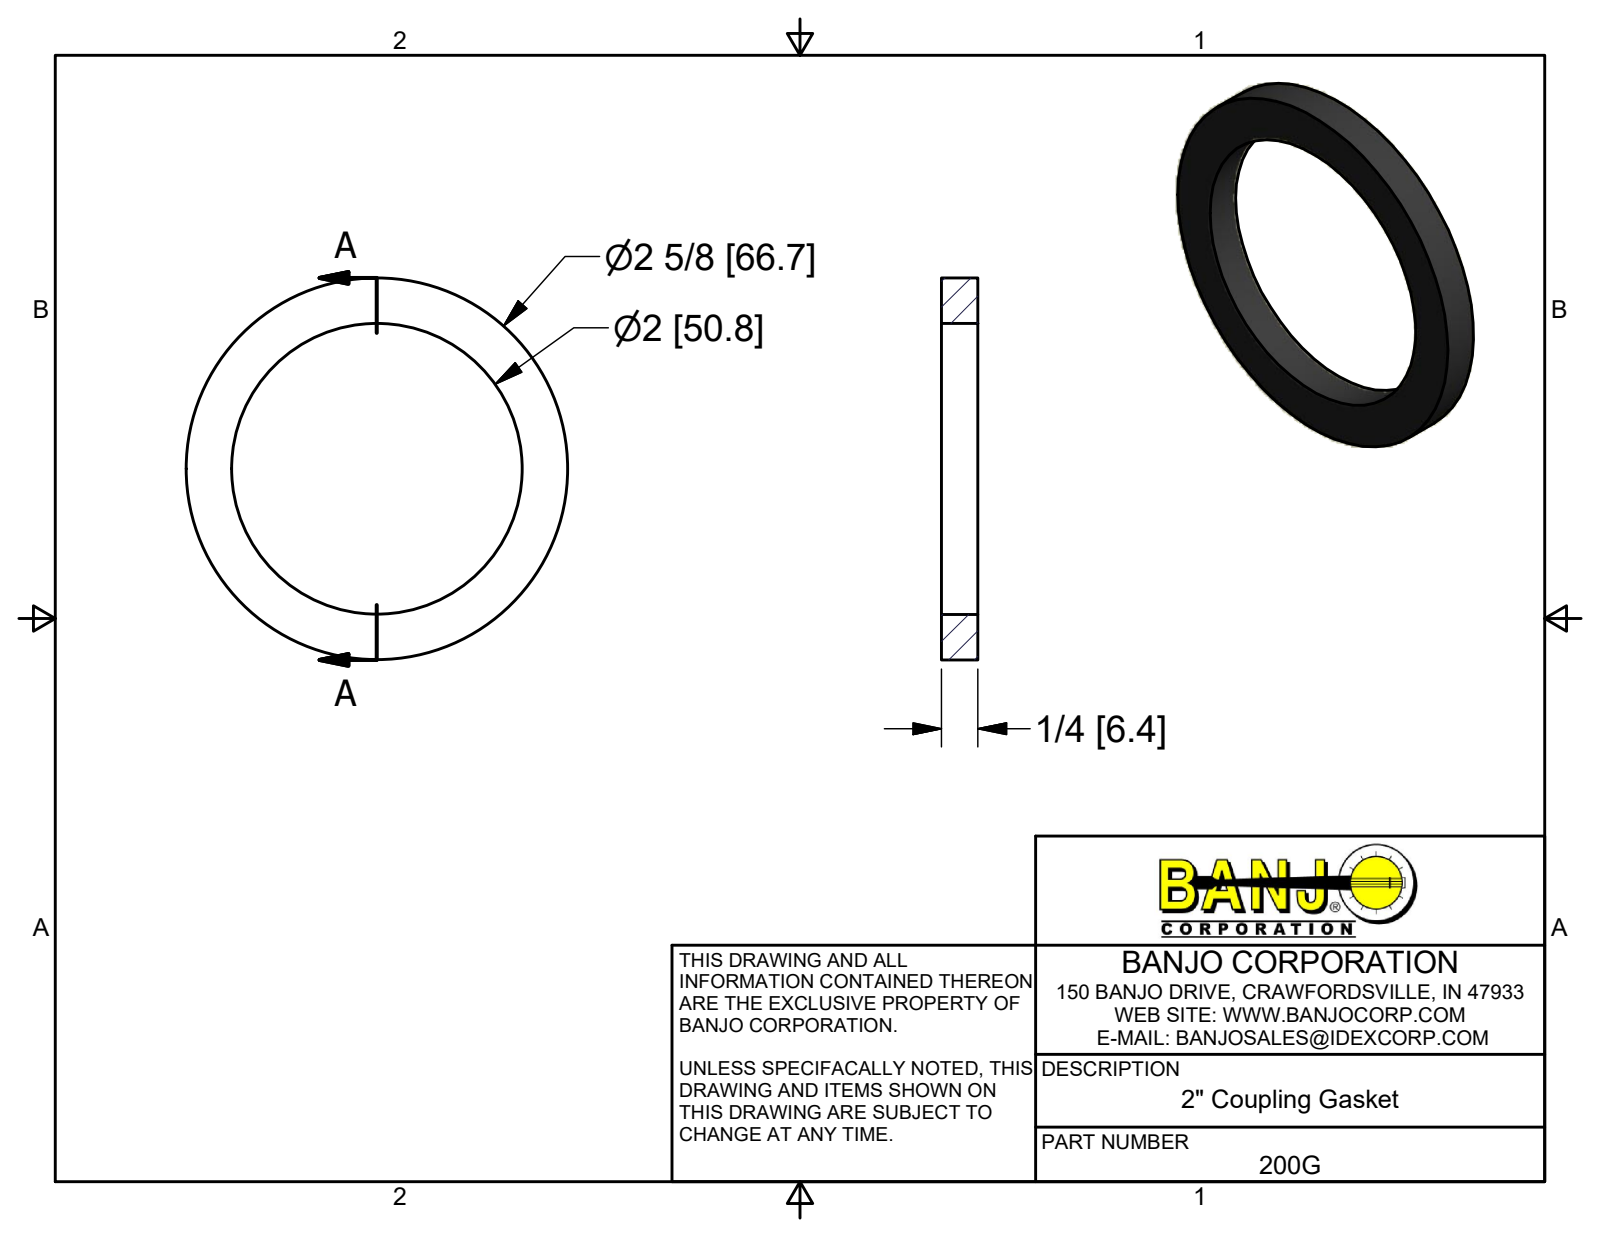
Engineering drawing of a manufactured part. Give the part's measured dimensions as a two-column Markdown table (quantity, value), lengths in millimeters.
| quantity | value |
| --- | --- |
| part name | 200G |
| STEP written by | Autodesk Inventor 2017 (AUTOMOTIVE_DESIGN) |
| units | millimeters |
| bodies | 1 solid, 4 faces (2 planar, 2 cylindrical, 0 other) |
| overall size | 66.67 × 66.67 × 6.35 |
| volume | 9 301 mm³ |
| surface area | 5 273 mm² |
| round holes (diameter × count) | 50.8 × 1 |
| round bosses / shafts (diameter × count) | 66.67 × 1 |
| main face-to-face distances | 6.34 |
